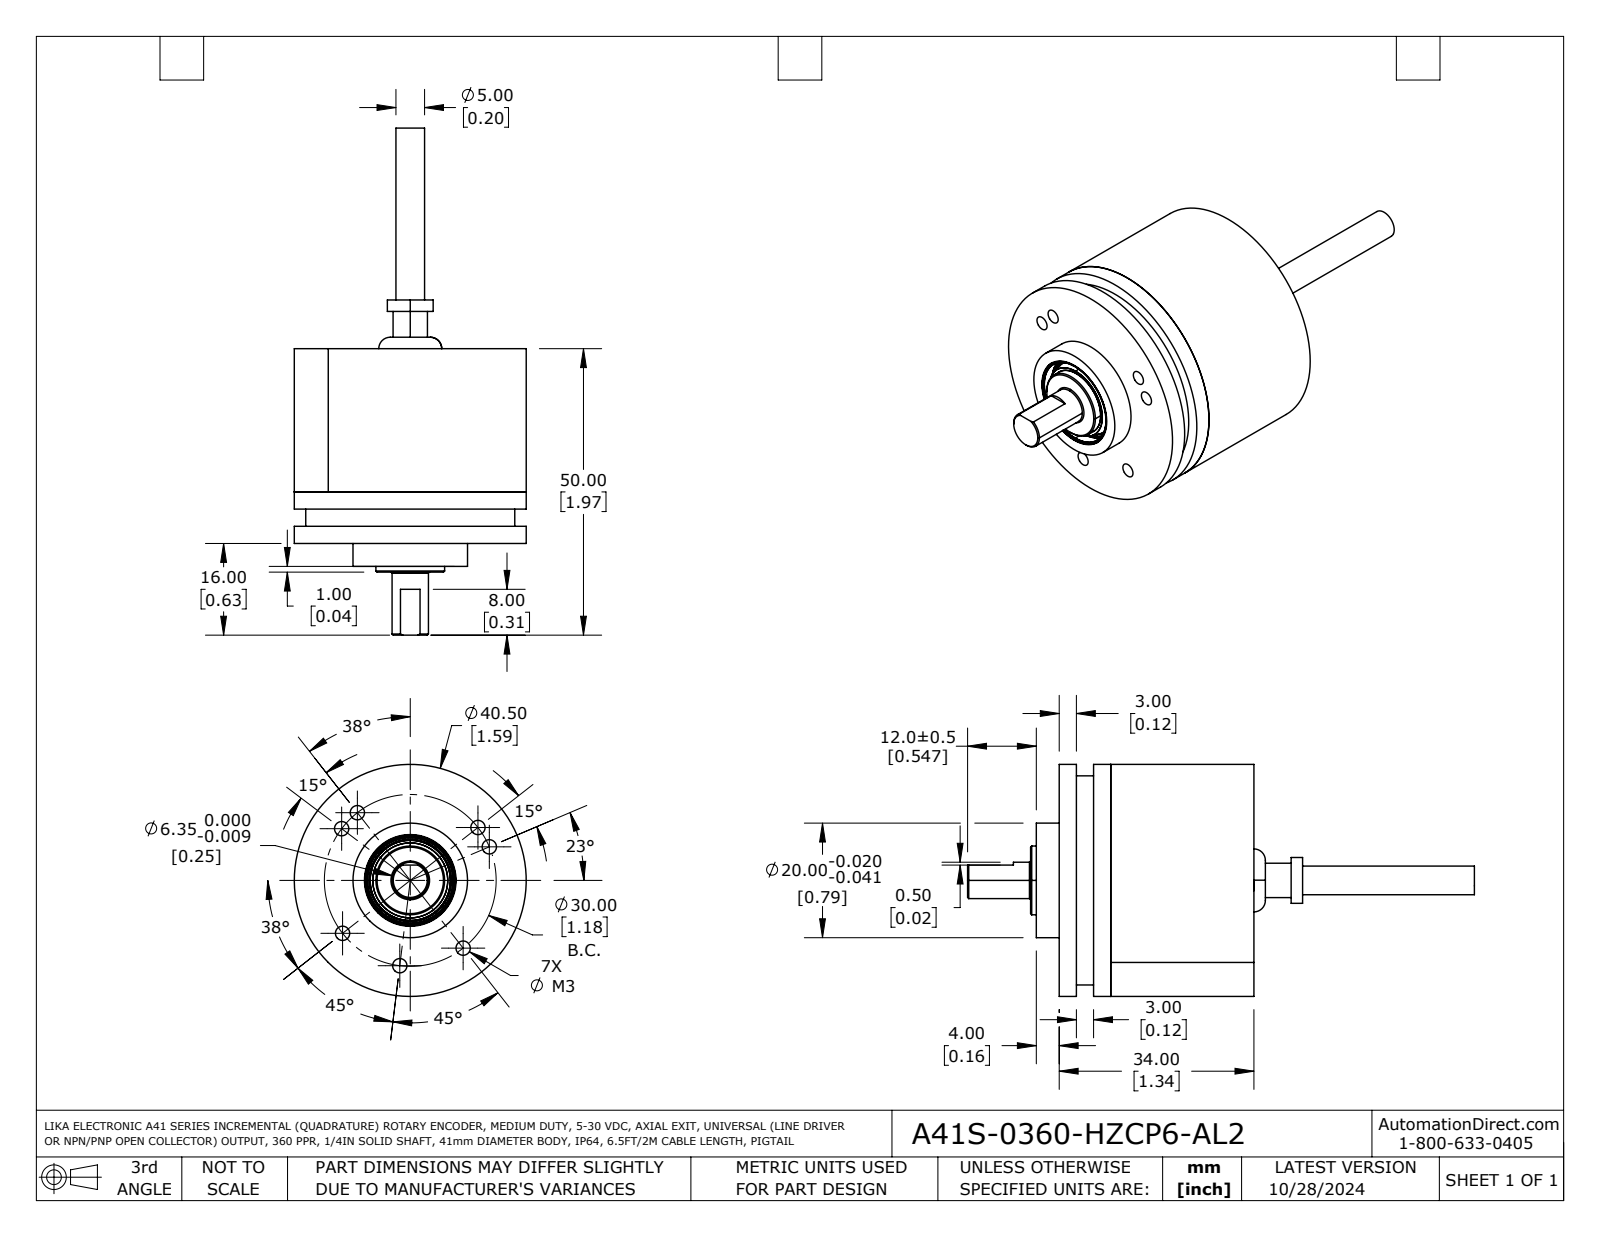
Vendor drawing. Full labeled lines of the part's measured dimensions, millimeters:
Part name (STEP PRODUCT): A41S-0360-HZCP6-AL2
STEP written by: SolidWorks 2021 (AUTOMOTIVE_DESIGN)
Units: millimetres
Bodies: 11 solids, 422 faces (76 planar, 145 cylindrical, 201 other)
Overall size (bounding box): 88.5 × 40.5 × 40.5
Volume: 19 250 mm³ · Surface area: 18 250 mm²
Round holes (diameter × count): ⌀1.6 ×7, ⌀2.5 ×7, ⌀4 ×3, ⌀2.2 ×2, ⌀4.3 ×1, ⌀7.5 ×1, ⌀13 ×1, ⌀15.3 ×1, ⌀15.5 ×1, ⌀16 ×1, ⌀38.5 ×1
Round bosses / shafts (diameter × count): ⌀2 ×2, ⌀40.5 ×1, ⌀38 ×1, ⌀37 ×1, ⌀36.5 ×1, ⌀20 ×1, ⌀12 ×1, ⌀8 ×1
Partial cylindrical surfaces — rounded edges, fillets, slot ends (radius × count): R1 ×14, R0.2 ×6, R0.2 ×2
Main face-to-face distances: 3, 34, 11, 23, 31, 2, 22, 25, 20, 1
Hole centre spacings: 15, 17, 21.2, 2.8, 3, 21.3, 24, 31.9
